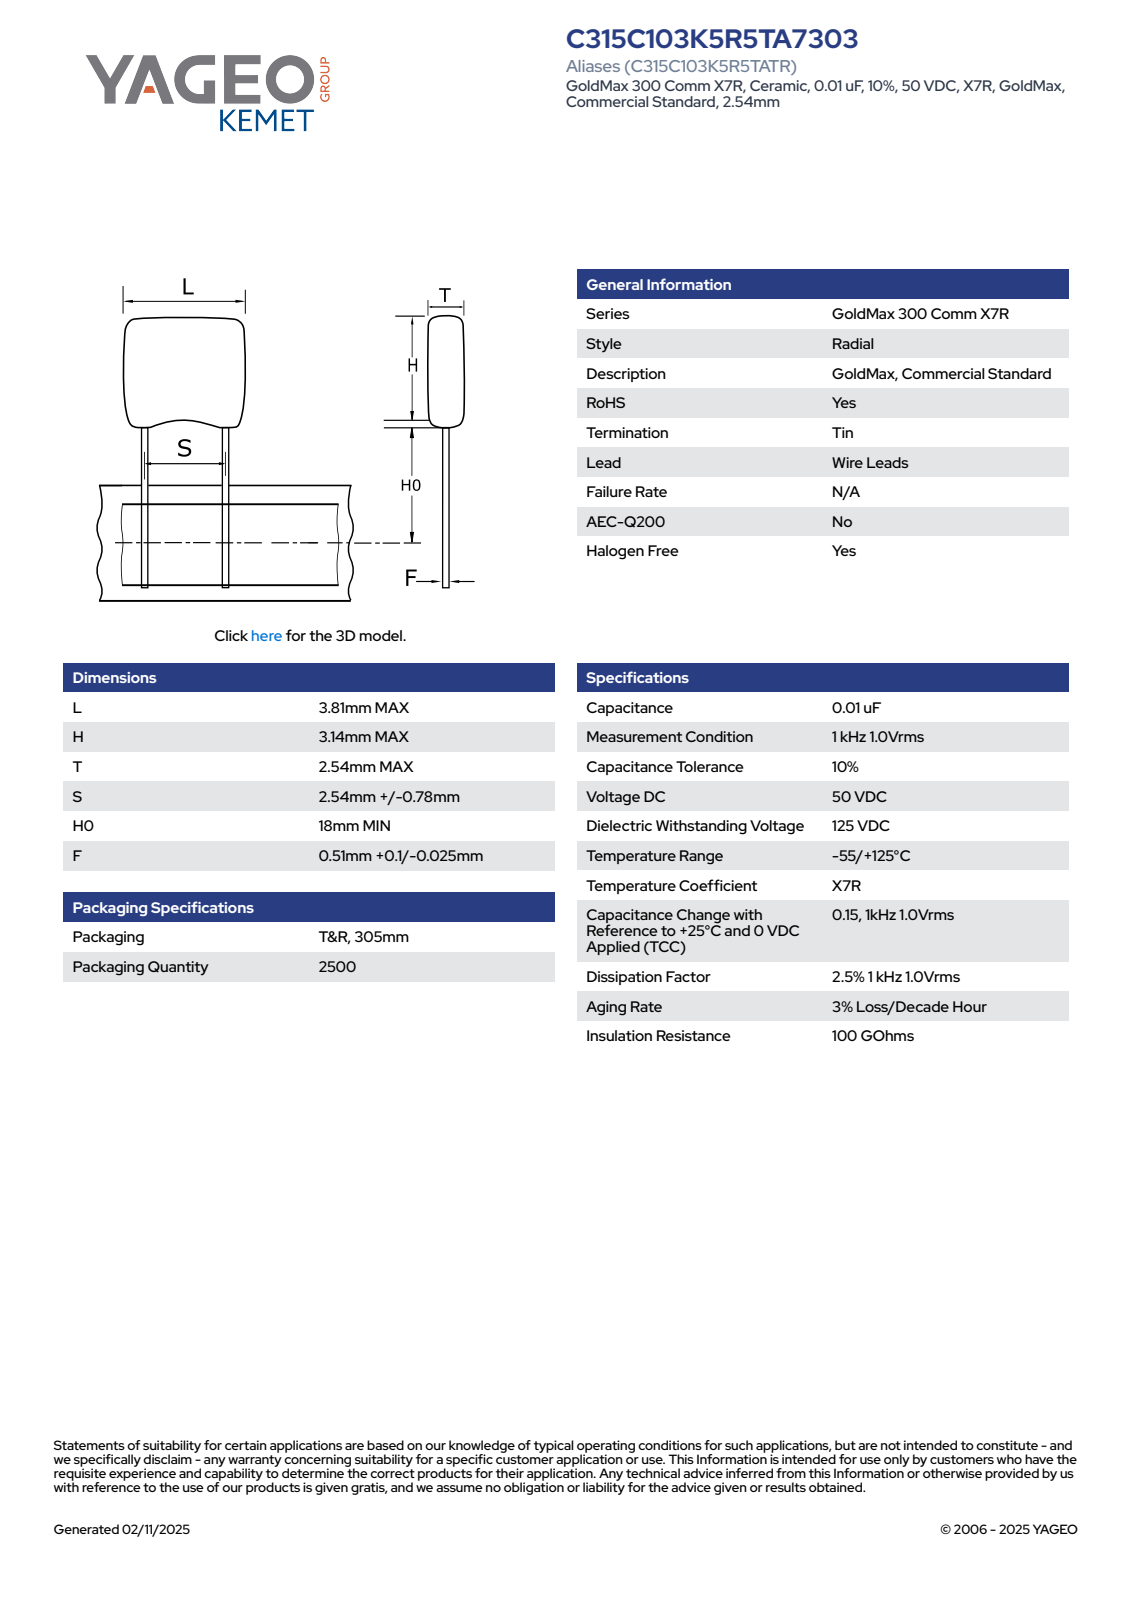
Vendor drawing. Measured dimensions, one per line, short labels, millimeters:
name: CCR_KRCST_3.81X3.14_L3.81H3.14T2.54S2.54H018F0.61
written by: SolidWorks 2014 (AUTOMOTIVE_DESIGN)
unit: mm
bodies: 4 solids, 83 faces (65 planar, 14 cylindrical, 4 other)
size: 21.5 × 3.81 × 2.54
volume: 41 mm³; area: 122 mm²
bosses: 2× ⌀0.61
rounds: 10× R0.75
face distances: 2.54, 3.81, 3.5, 18, 21.5, 0.41, 1.55, 19.96, 1.96, 1.54
